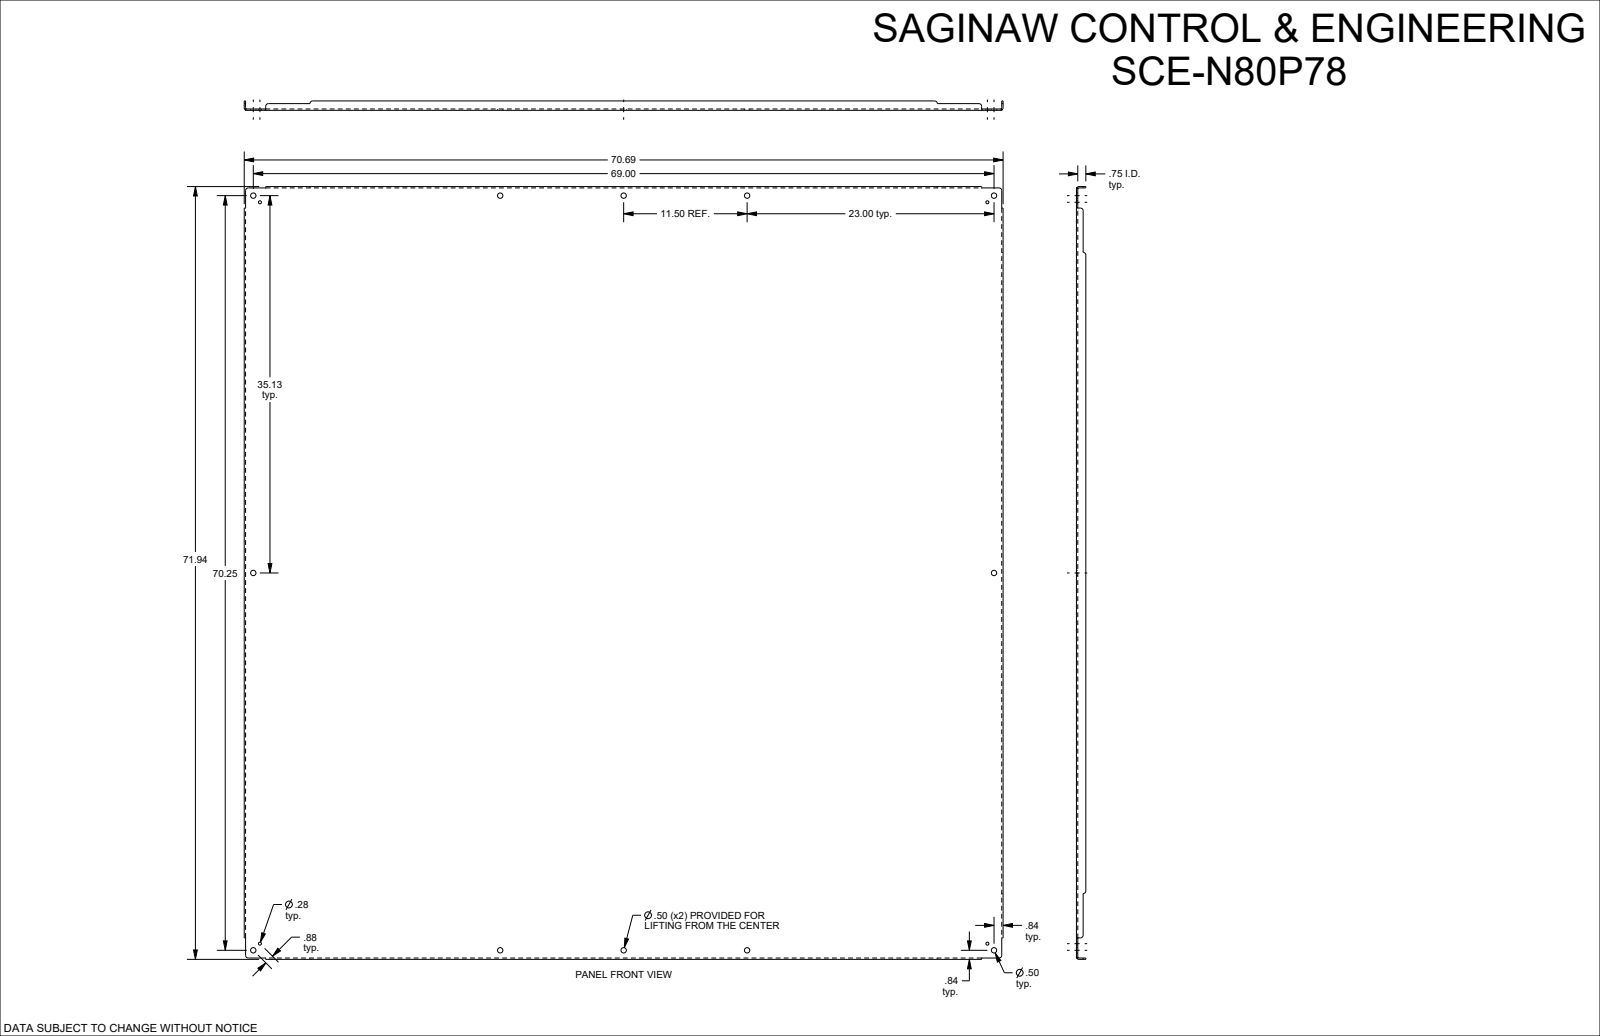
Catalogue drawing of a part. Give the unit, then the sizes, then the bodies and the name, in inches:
Units: inches
Overall size (bounding box): 71.938 × 70.688 × 0.875
Round holes (diameter × count): ⌀0.5 ×12, ⌀0.281 ×4
Partial cylindrical surfaces — rounded edges, fillets, slot ends (radius × count): R0.25 ×12, R0.112 ×4, R0.237 ×4
Main face-to-face distances: 0.125, 70.563, 0.125, 71.813, 70.438, 70.687, 71.687, 71.938, 0.75, 0.875
Hole centre spacings: 23, 73.919, 70.25, 0.875, 11.5, 22.39, 33.887, 34.5
Volume: 656.7 in³ · Surface area: 10 546 in²
Bodies: 1 solid, 130 faces (46 planar, 60 cylindrical, 24 other)
Part name (STEP PRODUCT): SCE-N80P78
STEP written by: SolidWorks 2023 (AUTOMOTIVE_DESIGN)
